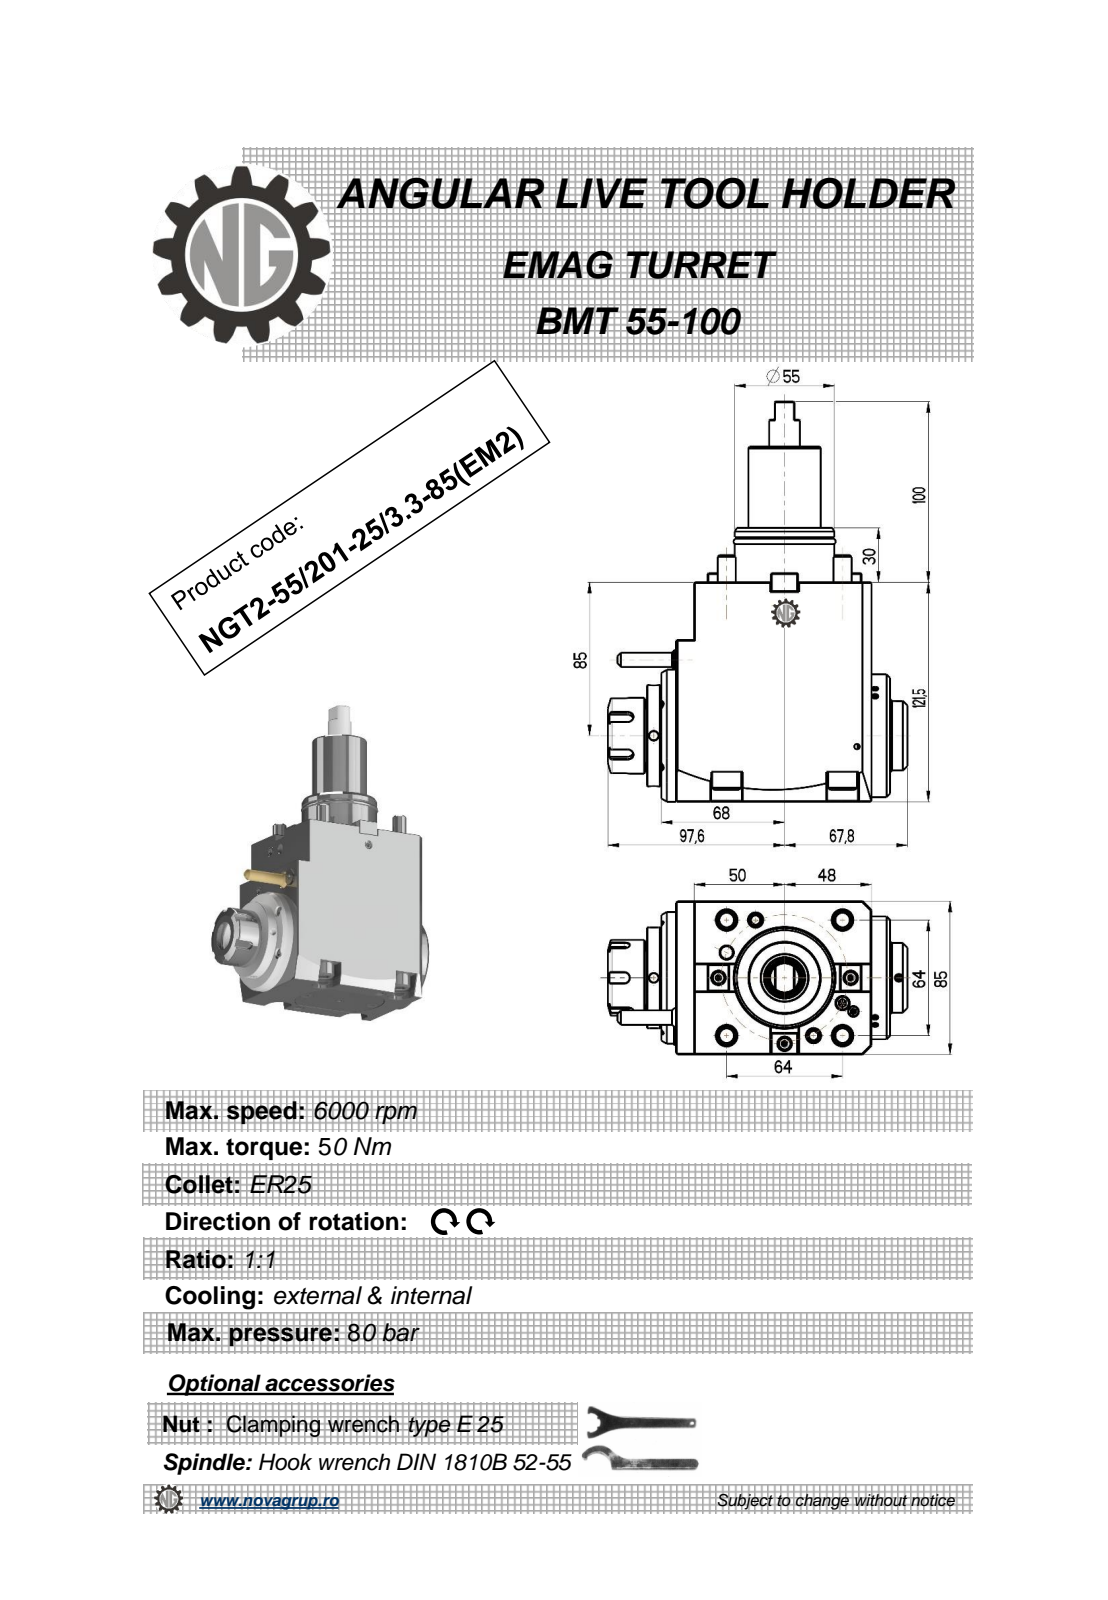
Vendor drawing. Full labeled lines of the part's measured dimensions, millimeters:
Part name (STEP PRODUCT): NGT2_55_201_25_3_3_85_EM2
STEP written by: PRO/ENGINEER BY PARAMETRIC TECHNOLOGY CORPORATION, 2010280 (CONFIG_CONTROL_DESIGN)
Units: millimetres
Bodies: 2 solids, 489 faces (229 planar, 111 cylindrical, 149 other)
Overall size (bounding box): 221.5 × 165.4 × 85
Volume: 1 323 000 mm³ · Surface area: 114 114 mm²
Round holes (diameter × count): ⌀5 ×3, ⌀6.8 ×2, ⌀3 ×1, ⌀12 ×1
Round bosses / shafts (diameter × count): ⌀16 ×4, ⌀10 ×4, ⌀73 ×1, ⌀68 ×1, ⌀56 ×1, ⌀55 ×1, ⌀50 ×1, ⌀43.4 ×1
Partial cylindrical surfaces — rounded edges, fillets, slot ends (radius × count): R0.32 ×20, R0.22 ×6, R3 ×5, R8.5 ×4, R0.8 ×2, R480 ×2
Main face-to-face distances: 85, 121.5, 8, 10, 108, 98, 18, 116, 108.3, 16
Hole centre spacings: 42.62, 69.86, 105.19
